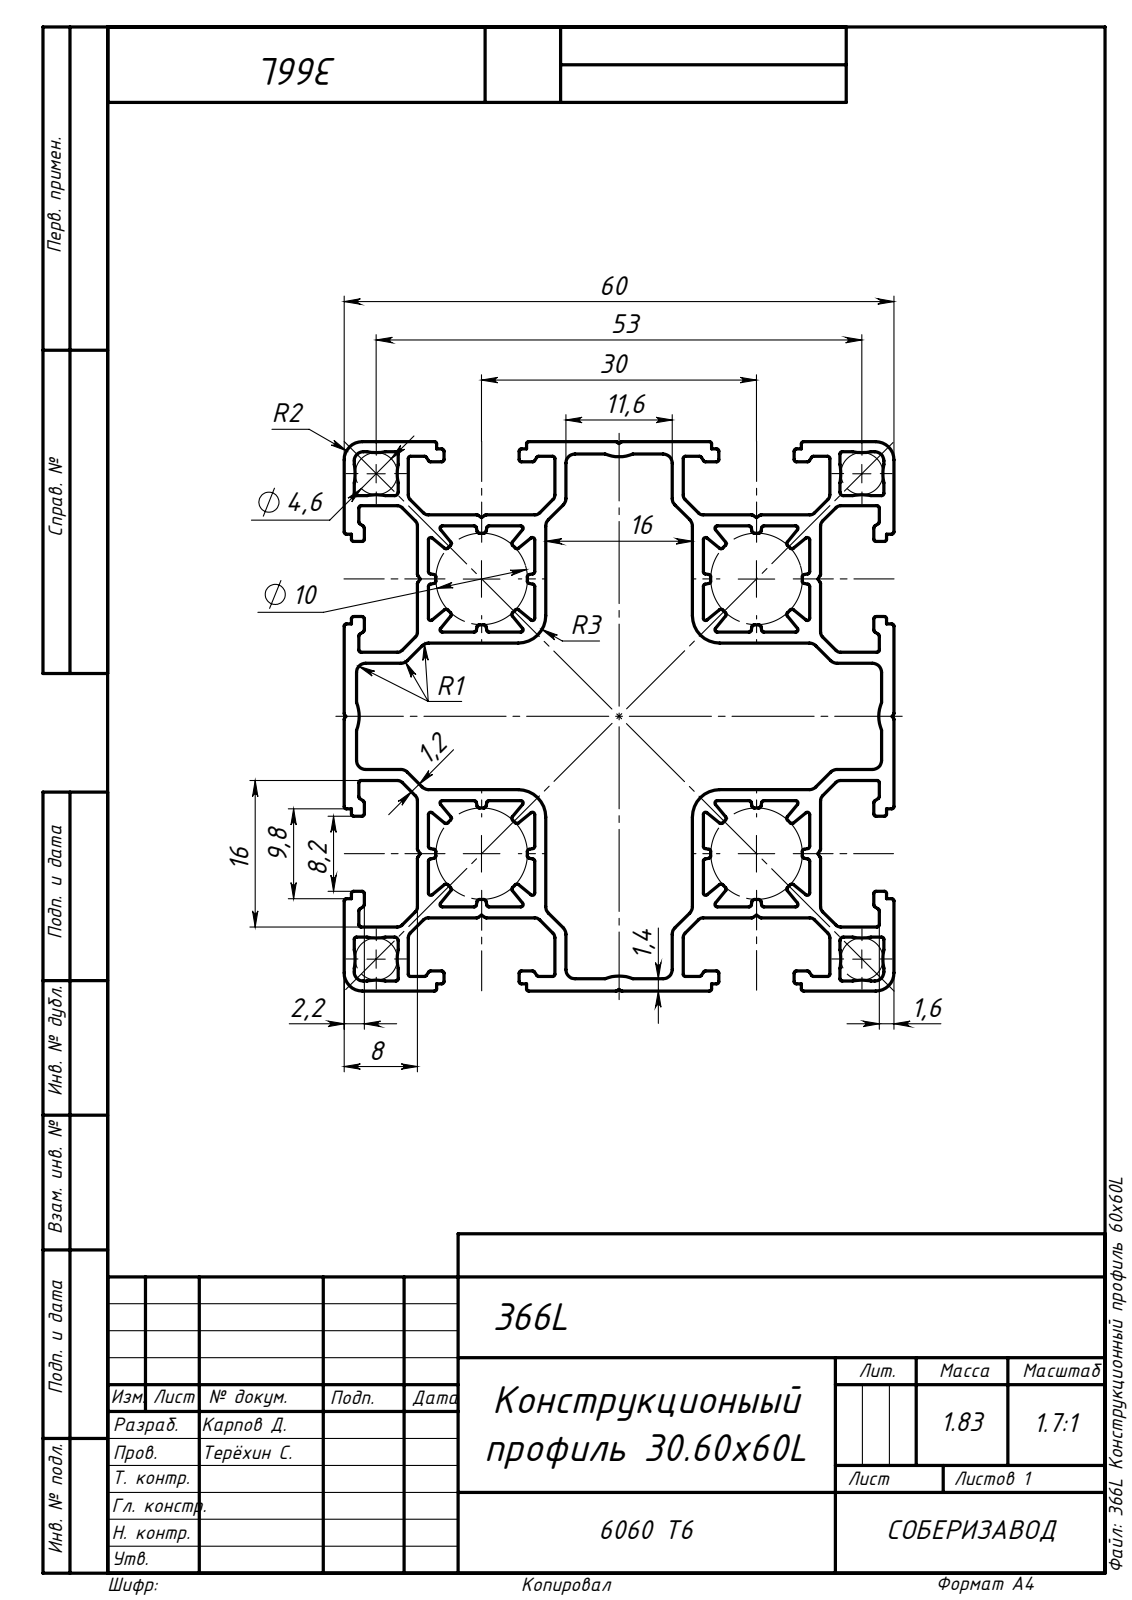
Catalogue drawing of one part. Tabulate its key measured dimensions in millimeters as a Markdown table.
| quantity | value |
| --- | --- |
| STEP written by | SolidWorks 2018 (AUTOMOTIVE_DESIGN) |
| units | millimeters |
| bodies | 1 solid, 790 faces (346 planar, 444 cylindrical, 0 other) |
| overall size | 1000 × 60 × 60 |
| volume | 679 357 mm³ |
| surface area | 1 012 000 mm² |
| partial cylindrical surfaces (radius × count) | 0.25 × 256, 0.75 × 32, 1 × 28, 5.05 × 16, 0.4 × 4, 2 × 4, 3 × 4, 4 × 4 |
| main face-to-face distances | 30, 15, 1.2, 12.8, 2.2, 13.8, 14, 17.2, 28.8, 8 |
